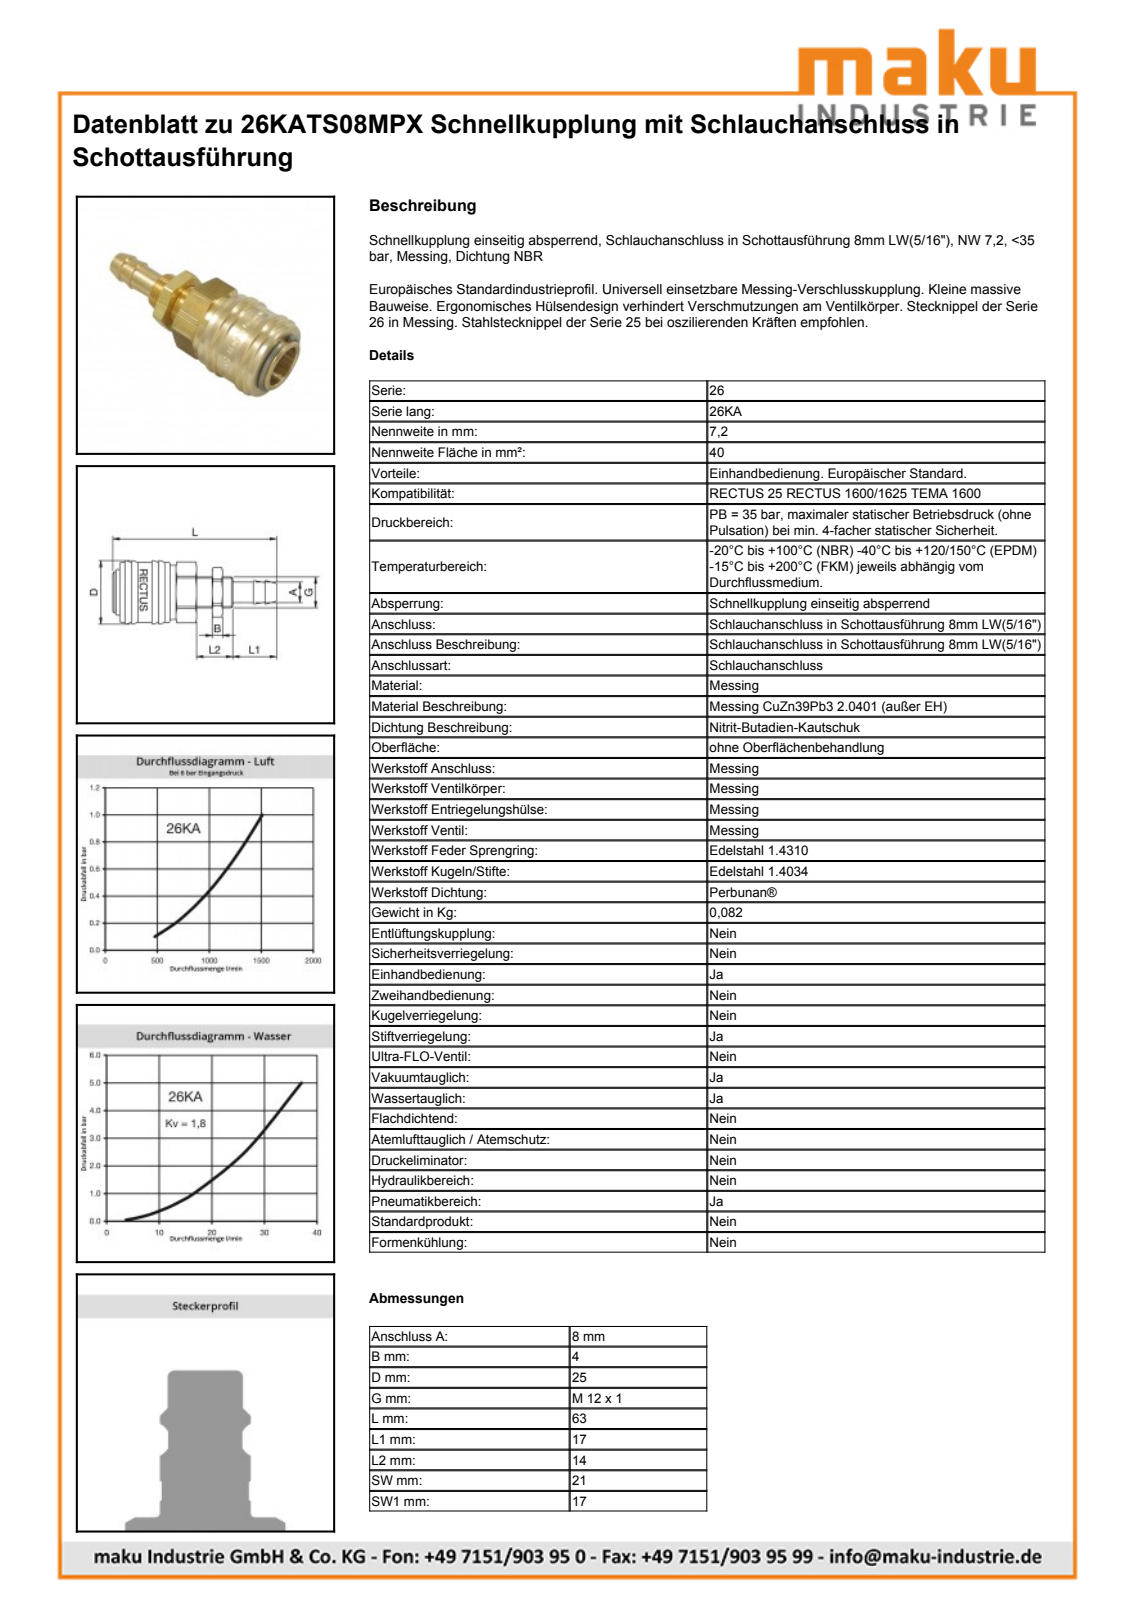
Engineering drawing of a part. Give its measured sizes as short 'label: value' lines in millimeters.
name: D107138
written by: Autodesk Inventor 2013 (AUTOMOTIVE_DESIGN)
unit: mm
bodies: 3 solids, 498 faces (184 planar, 70 cylindrical, 244 other)
size: 63 × 24.8 × 24.8
volume: 13 974 mm³; area: 8 126 mm²
holes: 1× ⌀15.45, 1× ⌀16.1, 1× ⌀17, 1× ⌀21.1
bosses: 1× ⌀23.3, 1× ⌀21, 1× ⌀18, 1× ⌀16.65, 1× ⌀15.95, 1× ⌀14.95, 1× ⌀14.8, 1× ⌀12
rounds: 1× R9.57, 1× R11.55, 1× R11.85
face distances: 21, 29.35, 2.65, 32, 17, 7.06, 4, 39.06, 36.41, 35.06
